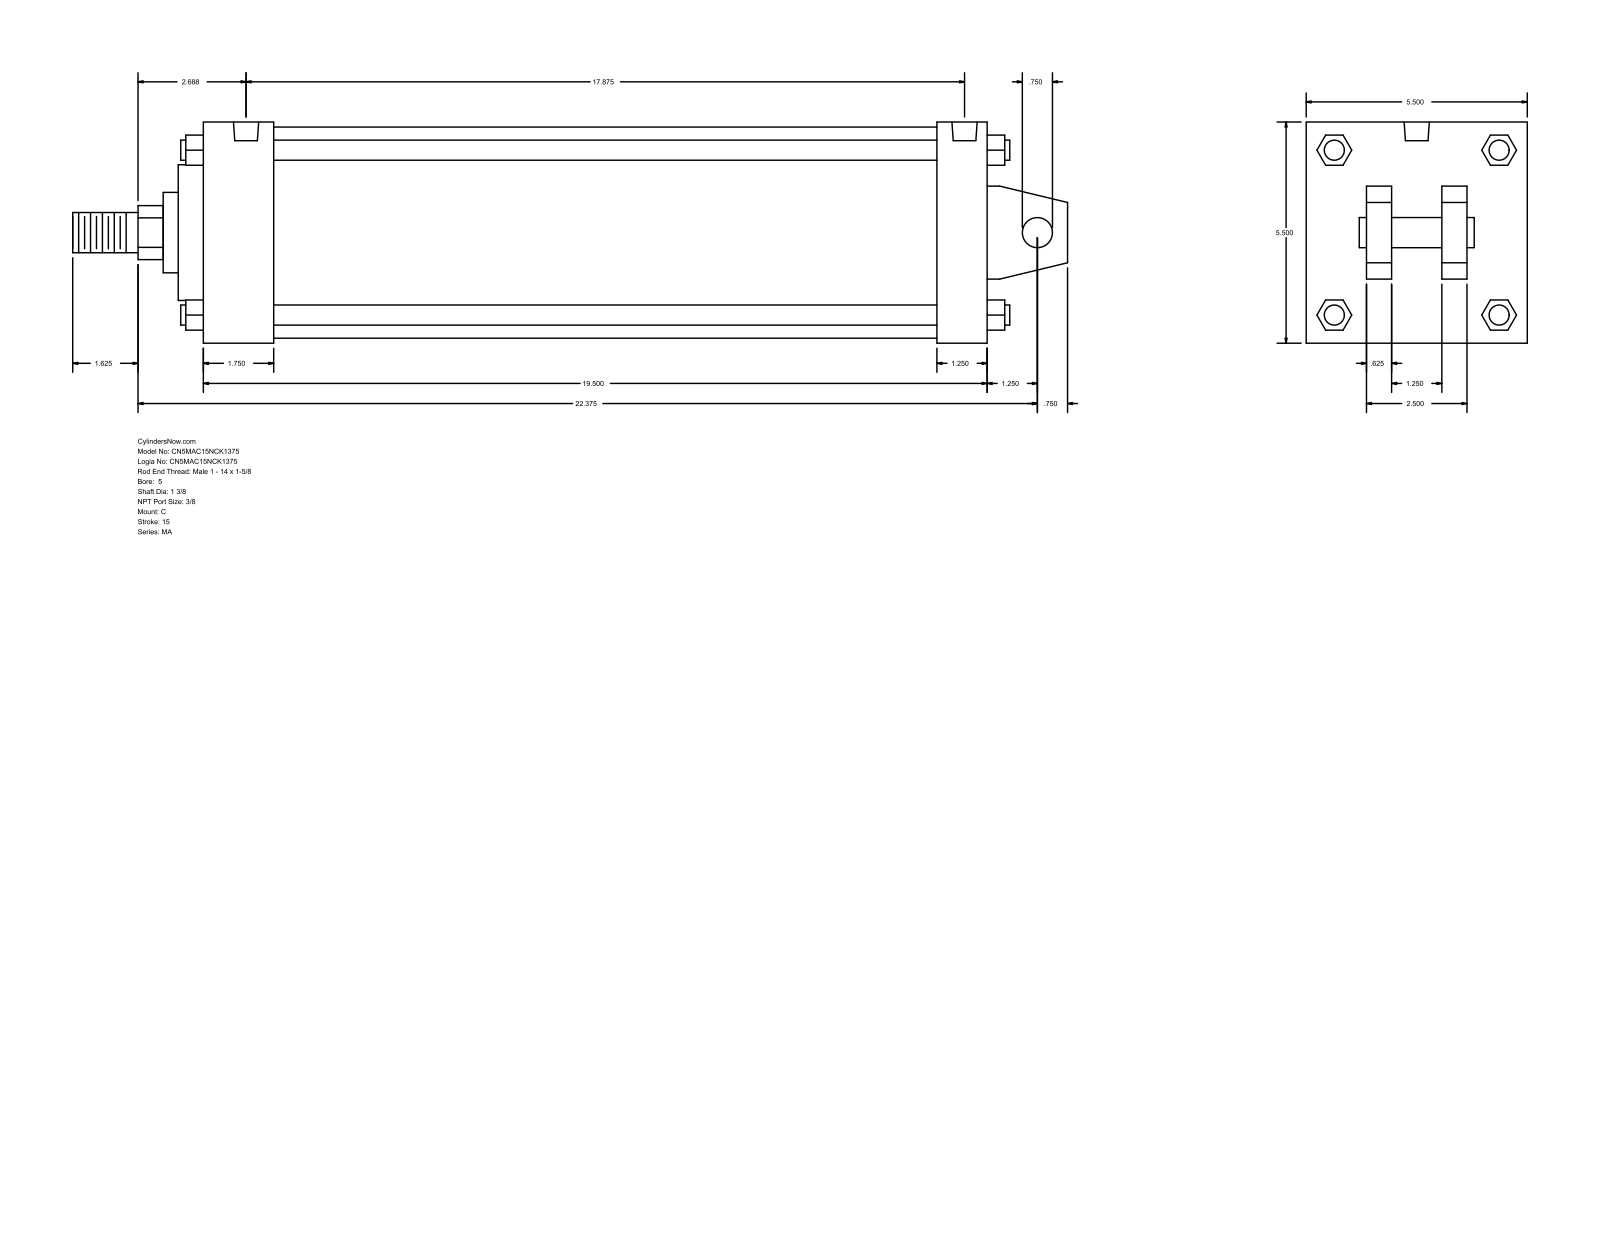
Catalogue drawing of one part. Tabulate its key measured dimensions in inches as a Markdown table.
| quantity | value |
| --- | --- |
| part name | MA_C__0500_1.375 |
| STEP written by | GSSL Pune (CONFIG_CONTROL_DESIGN) |
| units | inches |
| bodies | 0 solids, 141 faces (109 planar, 32 cylindrical, 0 other) |
| overall size | 24.75 × 5.5 × 5.5 |
| round holes (diameter × count) | 0.437 × 4, 0.627 × 2 |
| round bosses / shafts (diameter × count) | 0.5 × 4, 5.25 × 1, 3.375 × 1, 2 × 1, 1.375 × 1, 1 × 1, 0.75 × 1 |
| partial cylindrical surfaces (radius × count) | 0.672 × 1 |
| main face-to-face distances | 5.5, 19.5, 0.625, 1.25, 18.25, 1.75, 16.5, 17.75, 2.125, 1.5 |
| hole center spacings | 0.188, 17.5, 17.687, 17.875 |
